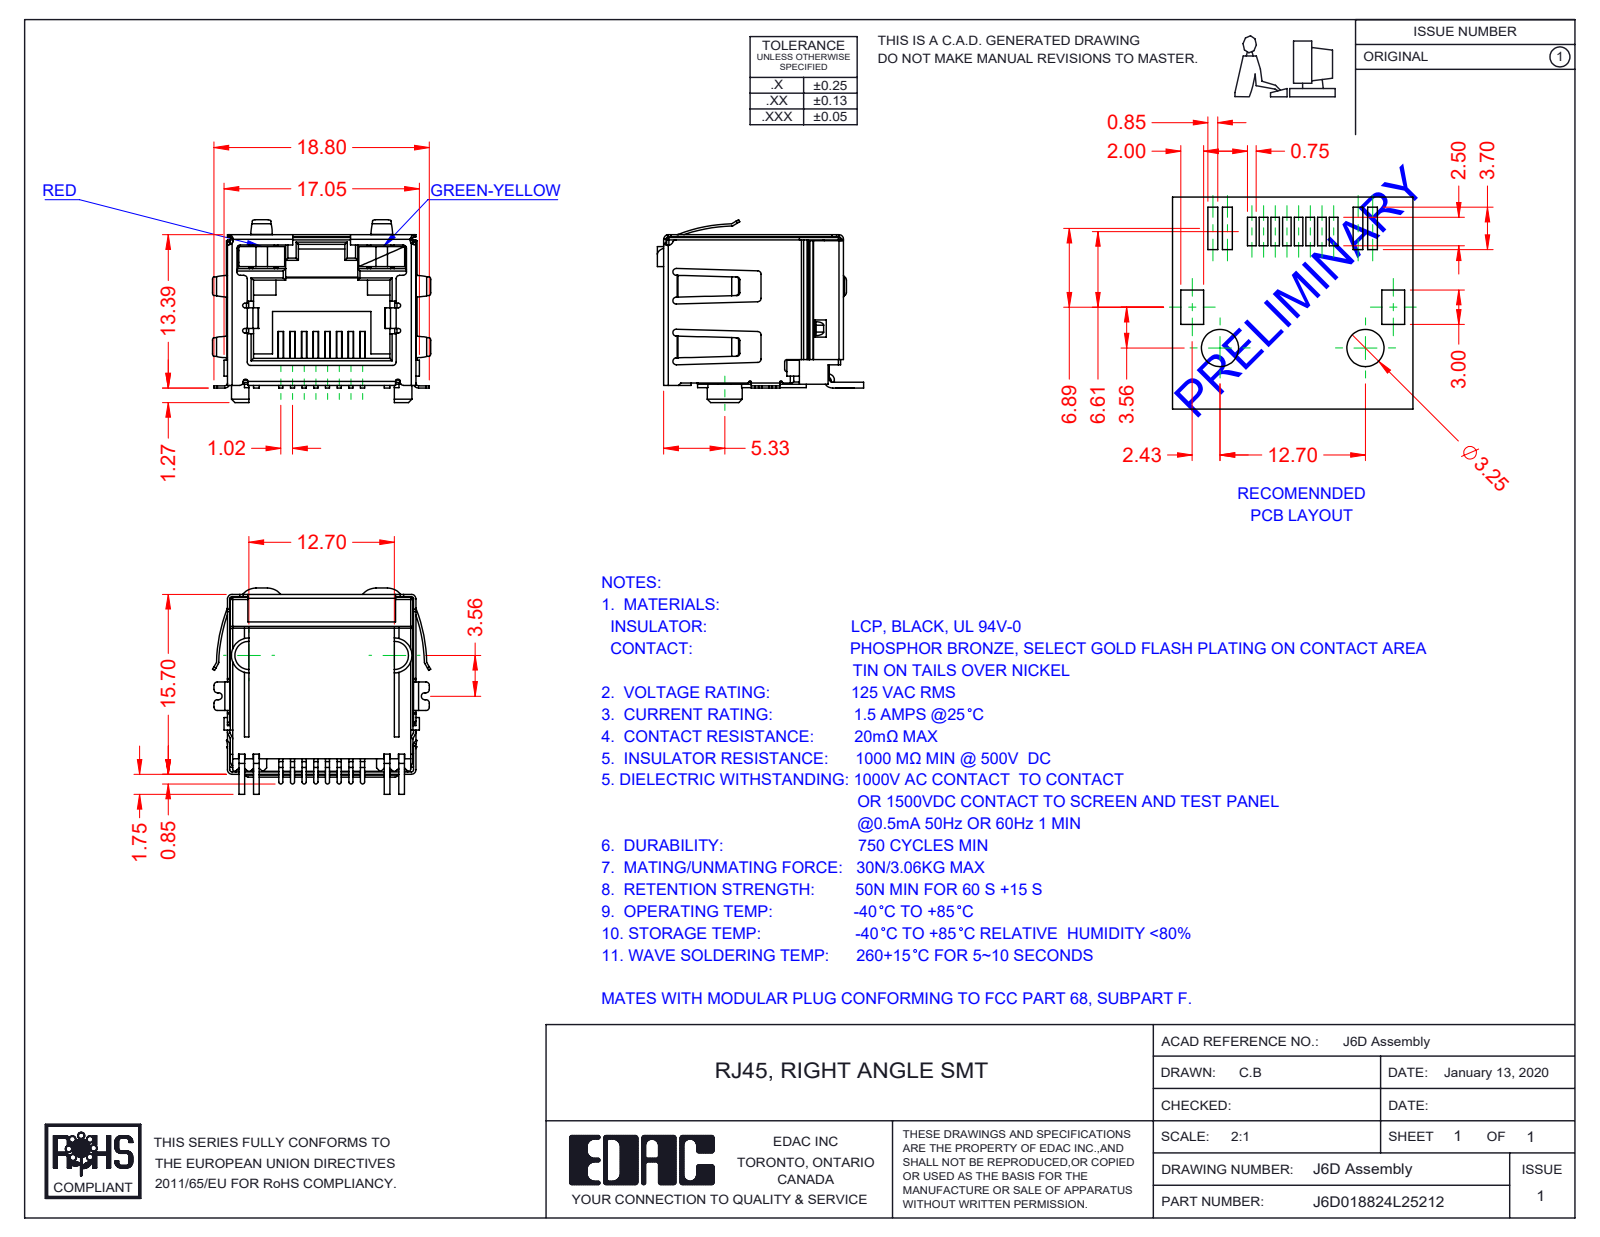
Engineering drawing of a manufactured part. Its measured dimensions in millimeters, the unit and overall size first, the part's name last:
Units: millimetres
Overall size (bounding box): 19.06 × 18 × 15.95
Partial cylindrical surfaces — rounded edges, fillets, slot ends (radius × count): R0.3 ×55, R0.2 ×40, R0.4 ×19, R0.25 ×16, R0.1 ×12, R0.15 ×8, R0.18 ×8, R0.5 ×6
Main face-to-face distances: 16, 16.2, 16.25, 2.25, 1, 15.95, 12.8, 0.45, 13.05, 10.6
Volume: 1 790 mm³ · Surface area: 4 796 mm²
Bodies: 12 solids, 1031 faces (702 planar, 284 cylindrical, 45 other)
Part name (STEP PRODUCT): 6D Shield_LED - EMI; J6D018824L25212; 6D LED RH_5-Green-Yellow; 6D LED LH_2-Red (+2 more)
STEP written by: SolidWorks 2016 (CONFIG_CONTROL_DESIGN)
